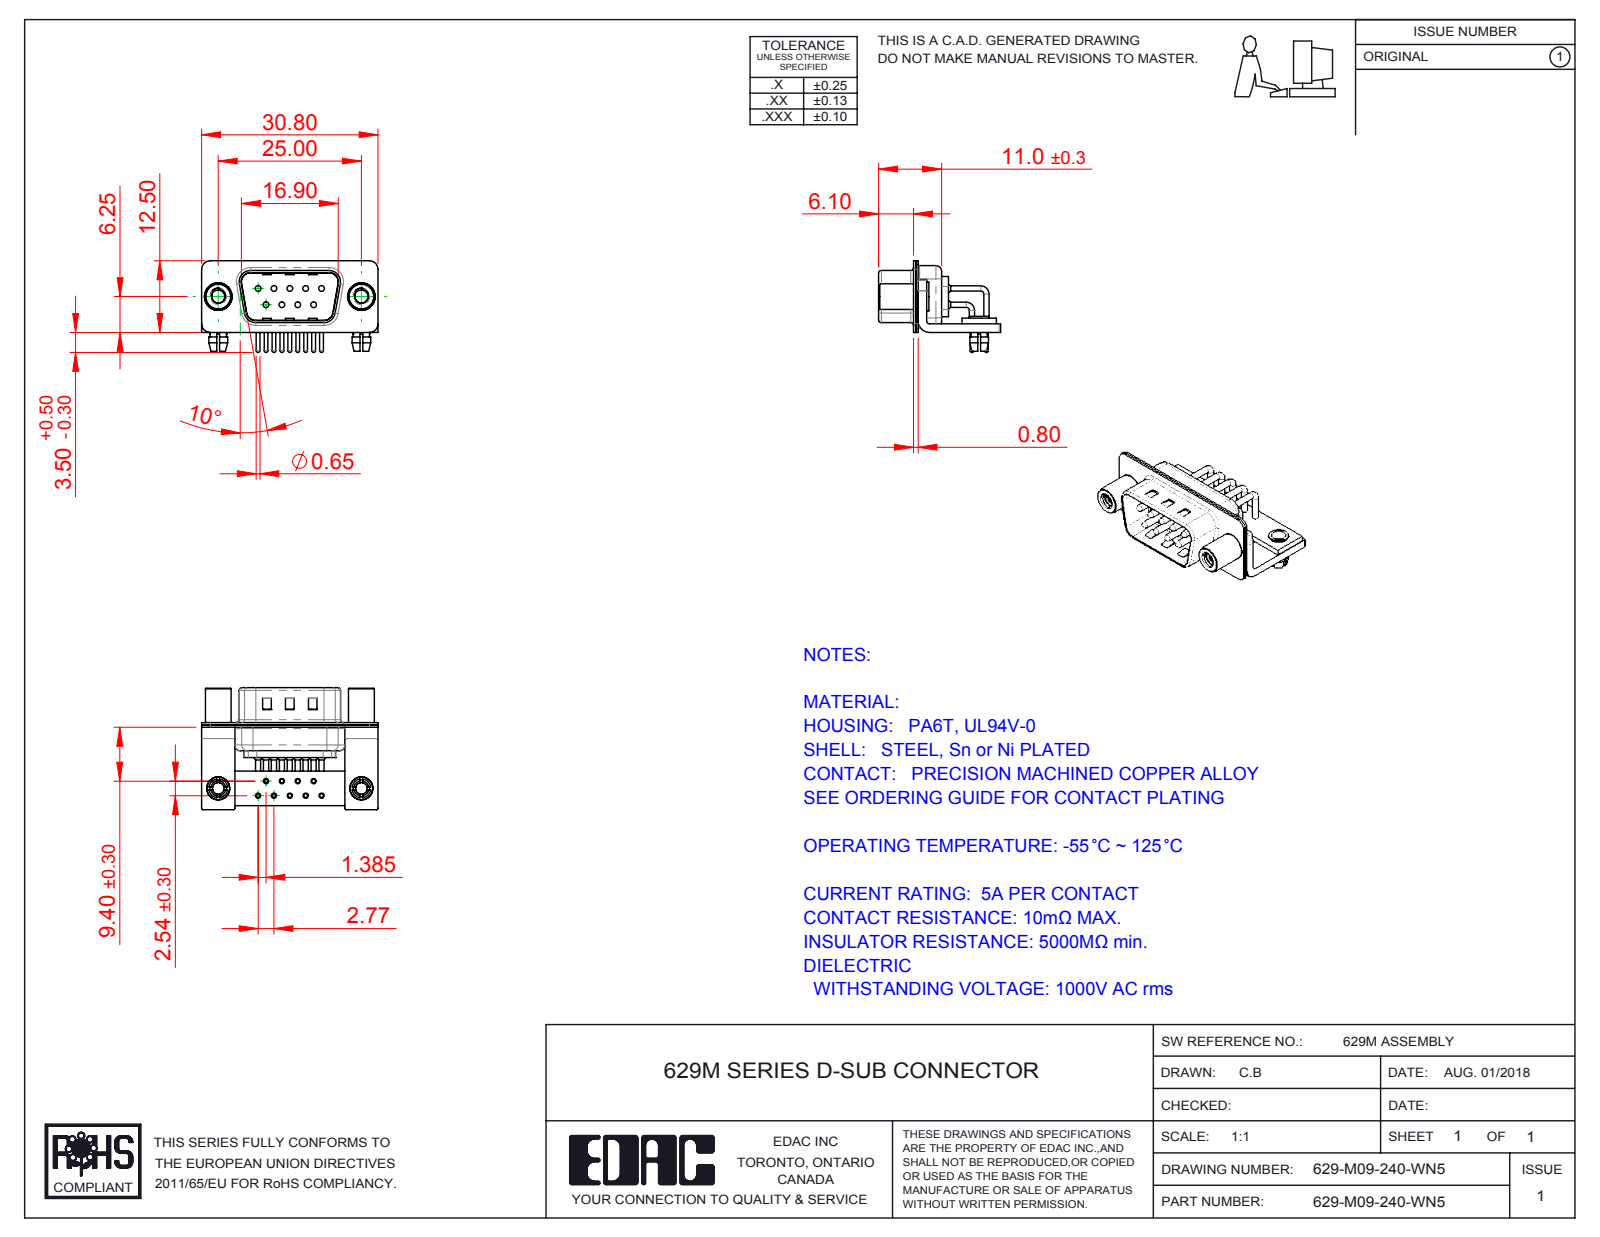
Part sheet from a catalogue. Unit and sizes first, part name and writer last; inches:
Units: inches
Overall size (bounding box): 1.213 × 0.839 × 0.63
Round holes (diameter × count): ⌀0.079 ×11, ⌀0.035 ×9, ⌀0.039 ×9, ⌀0.067 ×9, ⌀0.089 ×2, ⌀0.098 ×2, ⌀0.126 ×2, ⌀0.157 ×2, ⌀0.189 ×2
Round bosses / shafts (diameter × count): ⌀0.059 ×9, ⌀0.035 ×9, ⌀0.026 ×9, ⌀0.197 ×2, ⌀0.193 ×2, ⌀0.177 ×2, ⌀0.157 ×2, ⌀0.134 ×2
Partial cylindrical surfaces — rounded edges, fillets, slot ends (radius × count): R0.01 ×16, R0.059 ×16, R0.079 ×13, R0.02 ×9, R0.04 ×9, R0.063 ×8, R0.024 ×4, R0.026 ×4
Main face-to-face distances: 0.016, 0.059, 0.031, 0.033, 0.049, 0.075, 0.039, 0.098, 0.409, 0.376
Hole centre spacings: 0.109, 0.218, 0.124, 0.192, 0.327, 0.114, 0.114, 0.198
Volume: 0.121 in³ · Surface area: 8.541 in²
Bodies: 19 solids, 1504 faces (759 planar, 567 cylindrical, 178 other)
Part name (STEP PRODUCT): 629M Stabilizer Board_09 Contacts; 629M 4-40 Threaded Standoff; 629M Board Lock; 629M Contact Row 2 (+6 more)
STEP written by: SolidWorks 2016 (CONFIG_CONTROL_DESIGN)
